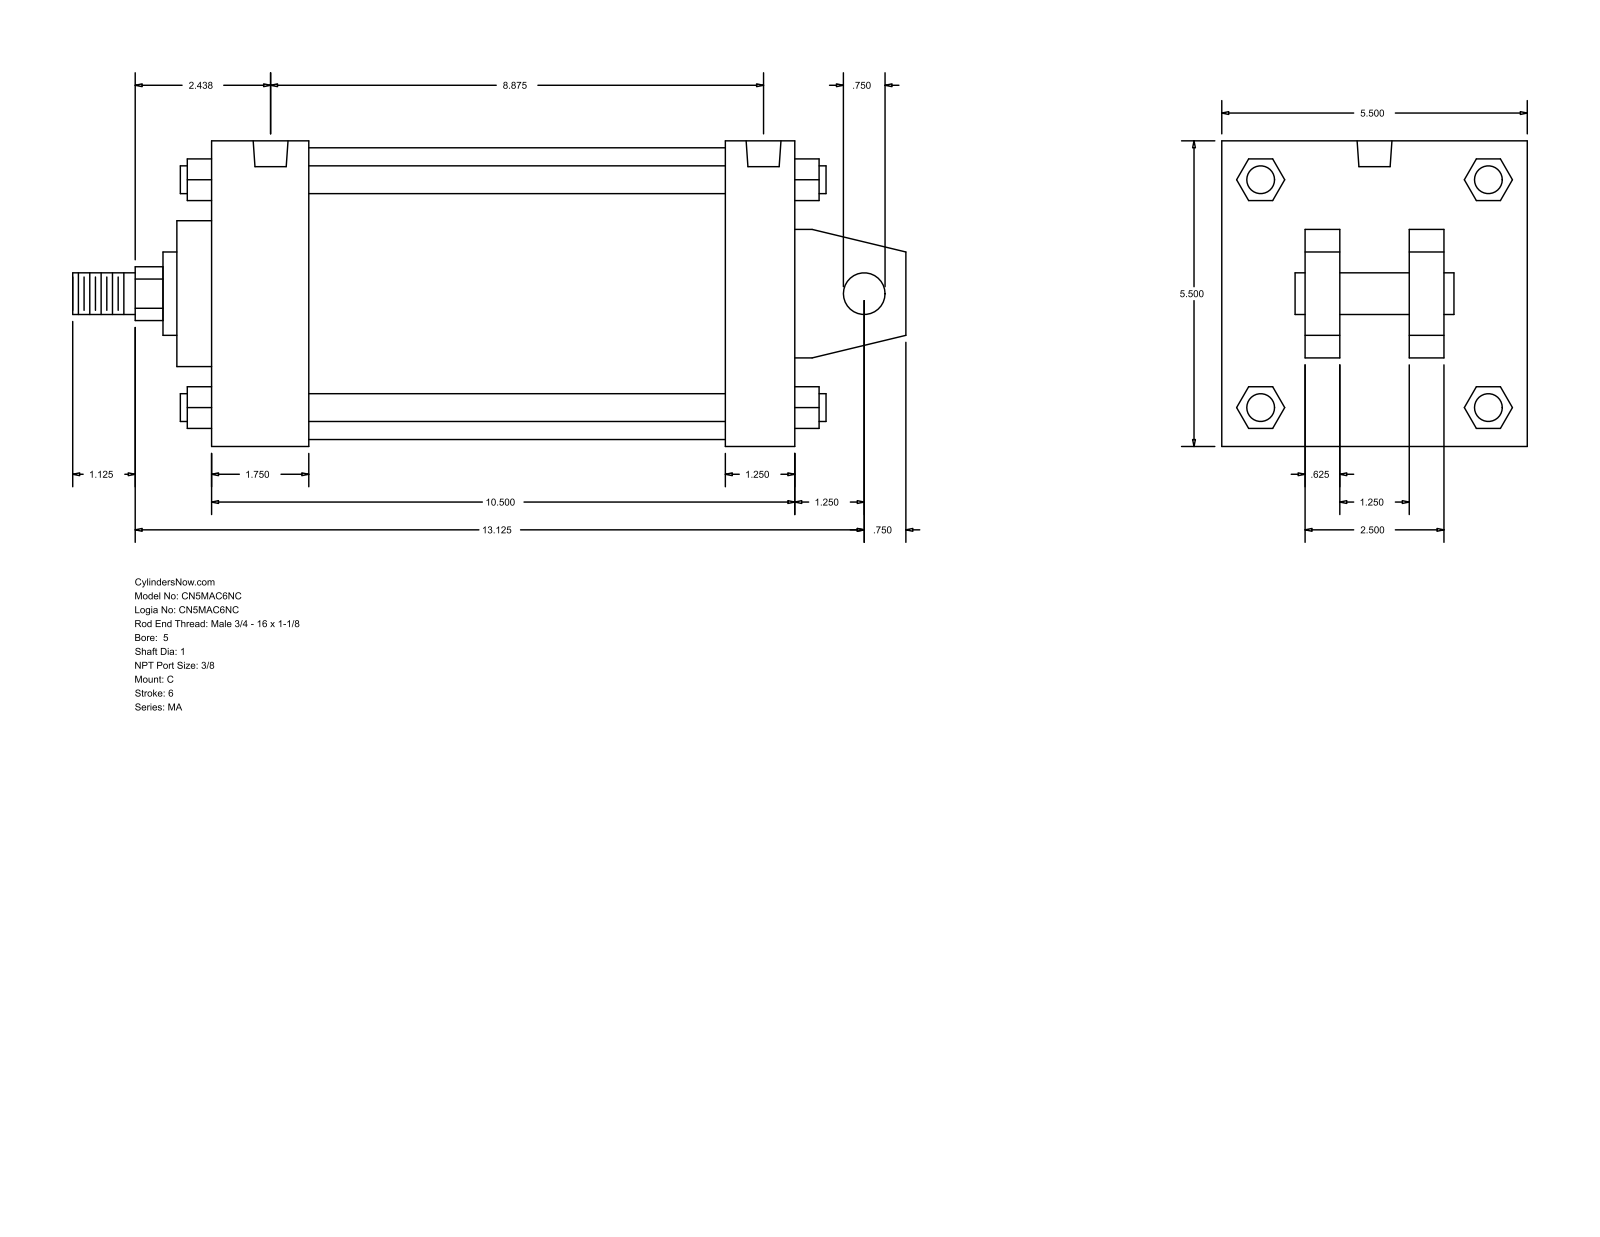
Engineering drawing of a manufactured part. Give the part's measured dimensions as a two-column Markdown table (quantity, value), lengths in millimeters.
| quantity | value |
| --- | --- |
| part name | MA_C__0500_1 |
| STEP written by | GSSL Pune (CONFIG_CONTROL_DESIGN) |
| units | millimeters |
| bodies | 0 solids, 141 faces (109 planar, 32 cylindrical, 0 other) |
| overall size | 381 × 139.7 × 139.7 |
| round holes (diameter × count) | 11.11 × 4, 15.93 × 2 |
| round bosses / shafts (diameter × count) | 12.7 × 4, 19.05 × 2, 133.35 × 1, 66.67 × 1, 38.1 × 1, 25.4 × 1 |
| partial cylindrical surfaces (radius × count) | 12.29 × 1 |
| main face-to-face distances | 139.7, 266.7, 15.87, 234.96, 31.74, 44.46, 190.5, 222.24, 38.1, 101.6 |
| hole center spacings | 215.9, 4.76, 4.77, 220.66, 220.67, 225.43 |
